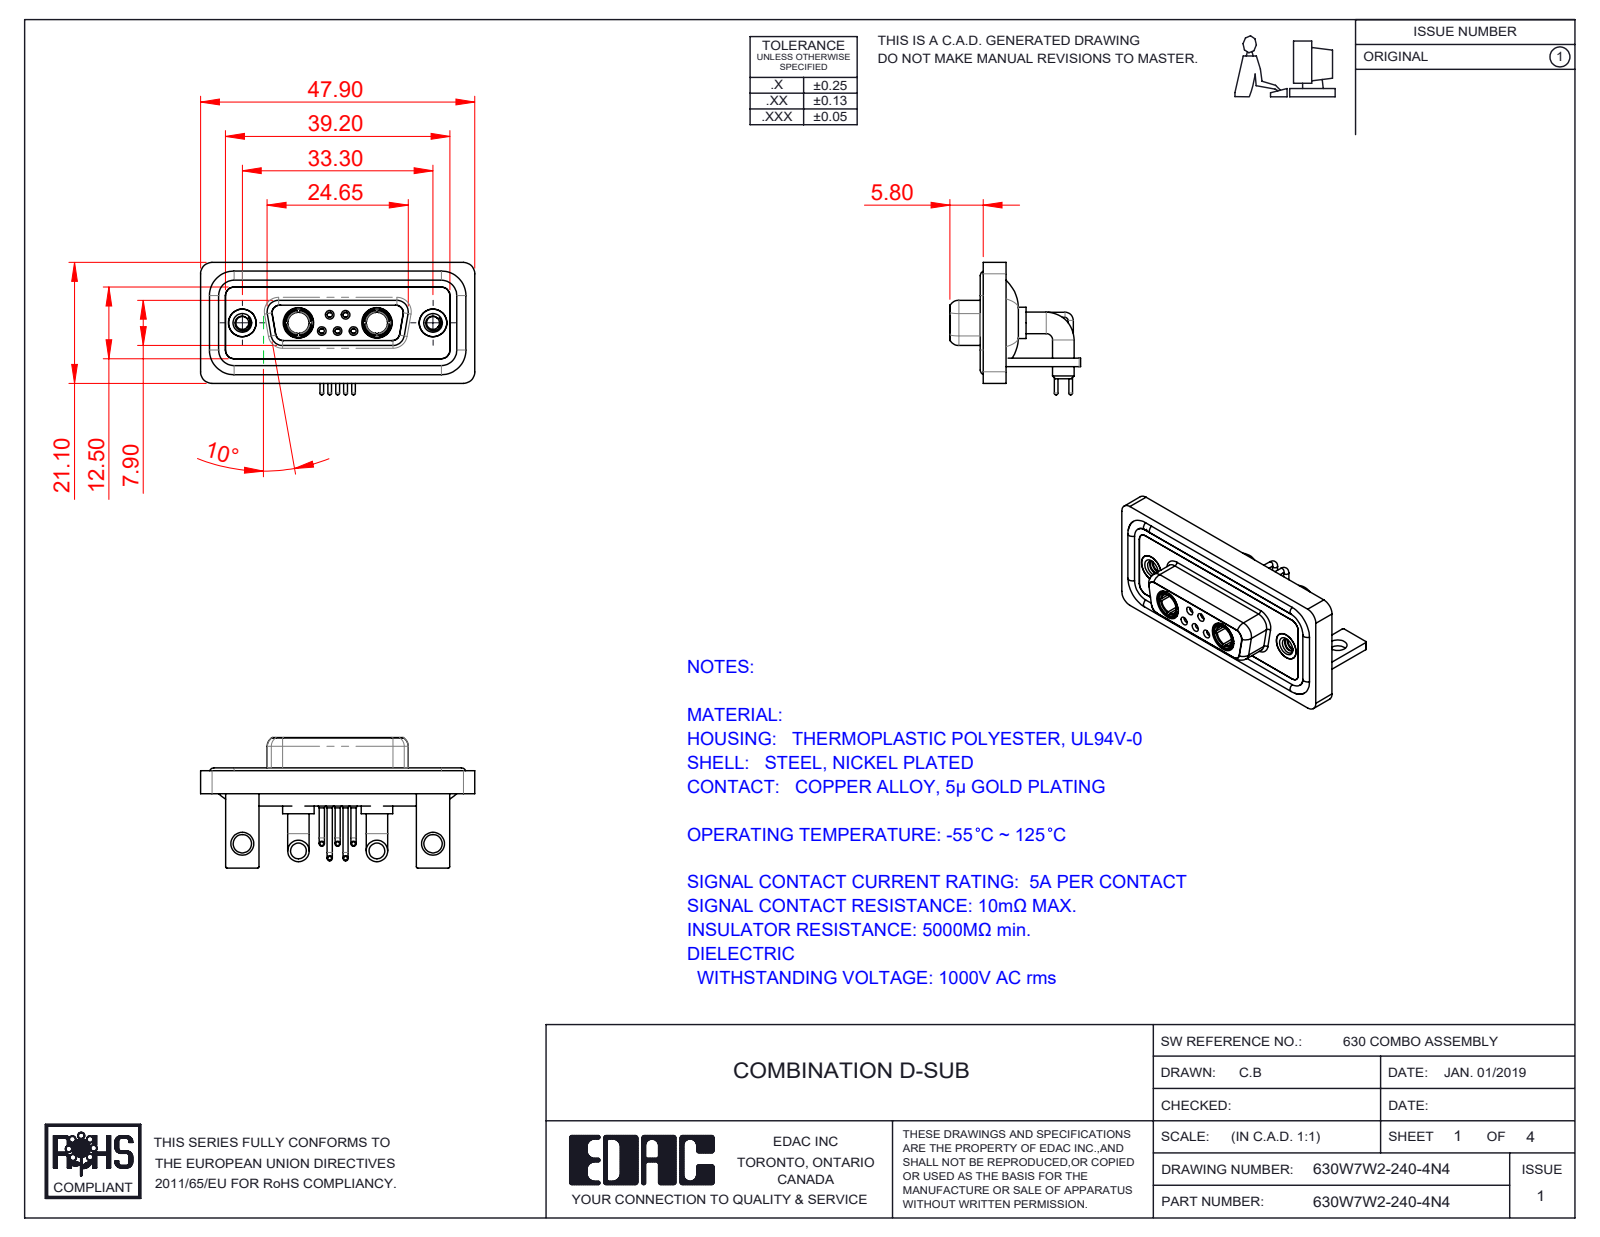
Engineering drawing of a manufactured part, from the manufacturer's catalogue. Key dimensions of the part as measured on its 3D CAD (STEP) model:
Part name (STEP PRODUCT): 630W7W2-140-4N4; 630Combo Shell Rear_15 Contacts; 630Combo Contact Row 1_50 Contacts; 630Combo Threaded Rivet_2 (+6 more)
STEP written by: SolidWorks 2023 (CONFIG_CONTROL_DESIGN)
Units: millimetres
Bodies: 18 solids, 855 faces (258 planar, 377 cylindrical, 220 other)
Overall size (bounding box): 47.9 × 23.12 × 22.8
Volume: 6 708 mm³ · Surface area: 11 028 mm²
Round holes (diameter × count): ⌀0.9 ×5, ⌀1.1 ×5, ⌀1.5 ×5, ⌀2 ×5, ⌀4.85 ×4, ⌀1.6 ×3, ⌀1.7 ×2, ⌀2.26 ×2, ⌀3.2 ×2, ⌀3.7 ×2, ⌀4 ×2, ⌀4.05 ×2
Round bosses / shafts (diameter × count): ⌀1.6 ×6, ⌀0.9 ×5, ⌀0.65 ×5, ⌀3.75 ×4, ⌀5.5 ×2, ⌀5.2 ×2, ⌀4.96 ×2, ⌀4.95 ×2
Partial cylindrical surfaces — rounded edges, fillets, slot ends (radius × count): R2 ×21, R1.5 ×18, R0.25 ×16, R1.35 ×12, R1.6 ×8, R0.5 ×5, R0.6 ×4, R0.65 ×4
Main face-to-face distances: 0.4, 2.9, 1.5, 1.8, 3.7, 1.1, 4.1, 1.6, 2.5, 1.4
Hole centre spacings: 3.16, 2.77, 9.8, 23.5, 33.3, 4.31, 4.33, 5.03
